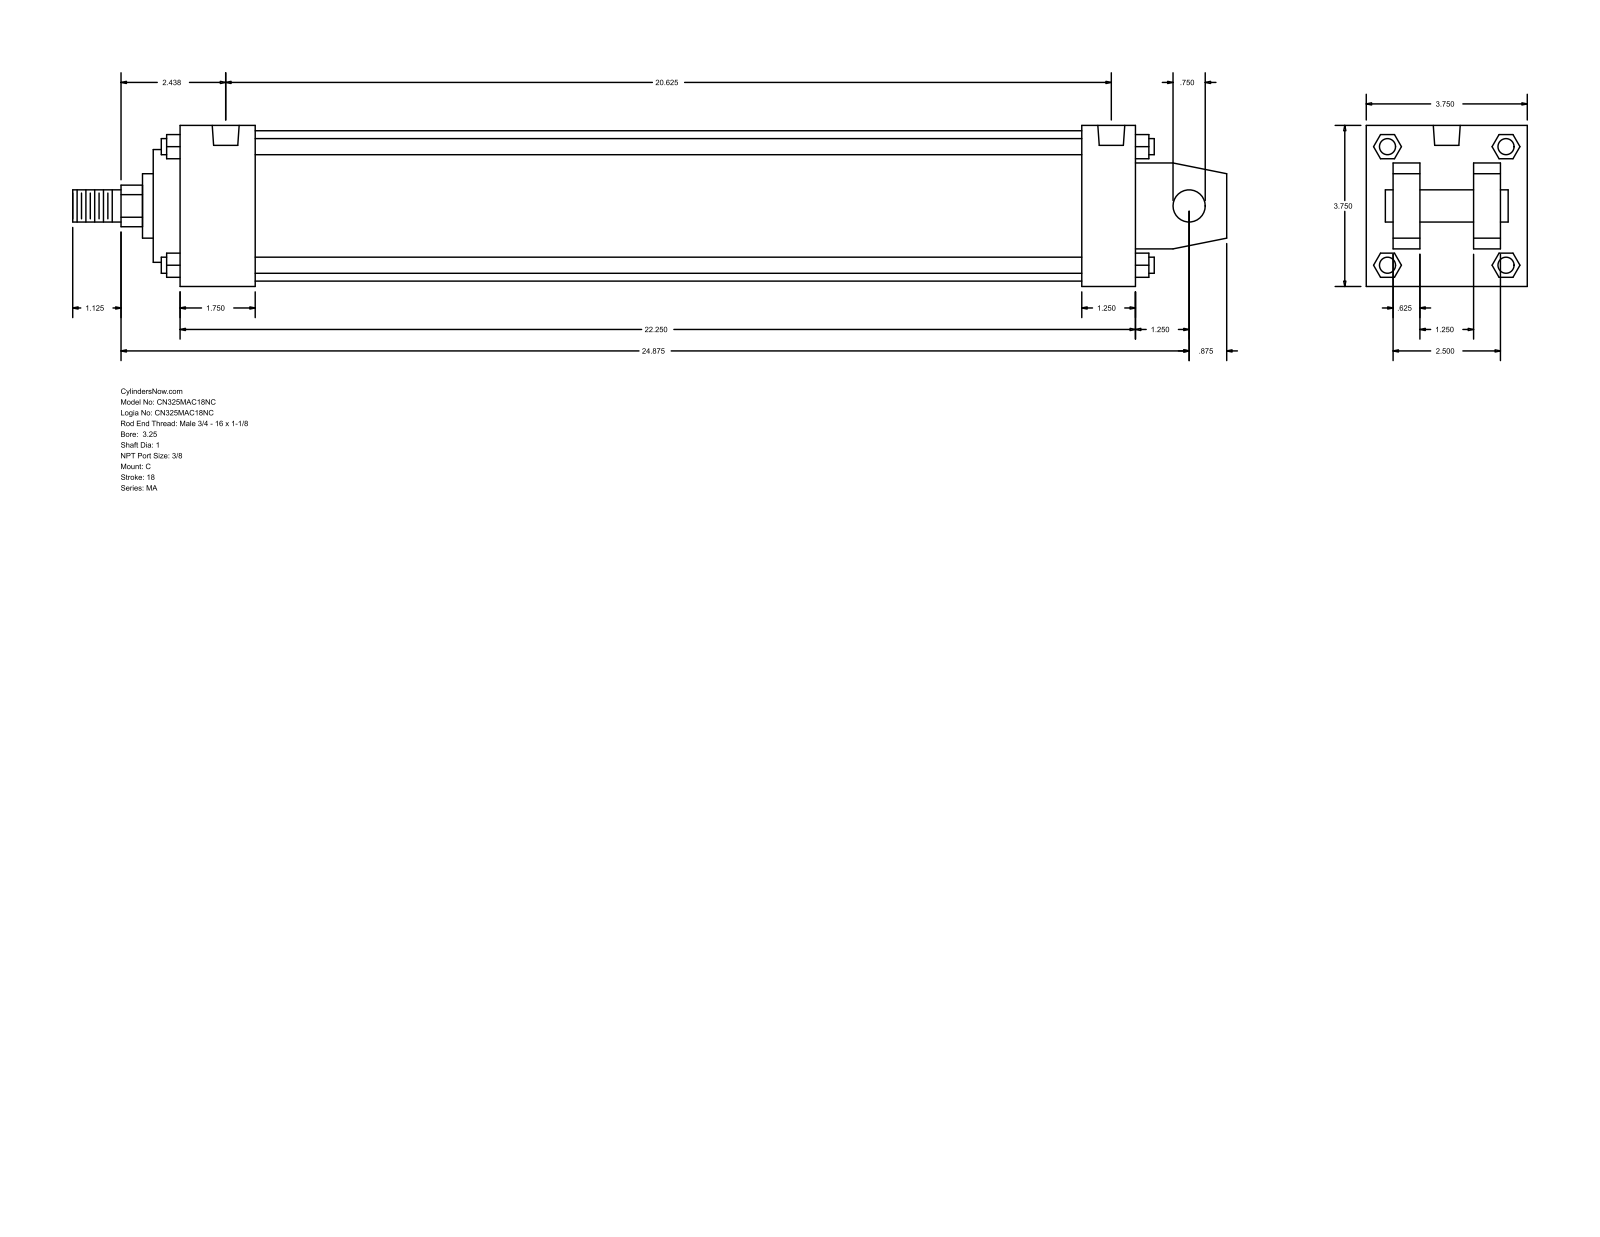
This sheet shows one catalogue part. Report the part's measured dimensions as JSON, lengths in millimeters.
{"part_name": "MA_C__0325_1", "step_written_by": "GSSL Pune (CONFIG_CONTROL_DESIGN)", "units": "millimeters", "bodies": {"solids": 0, "faces": 141, "planar": 109, "cylindrical": 32, "other": 0}, "overall_size": [682.62, 95.25, 95.25], "round_holes": [[11.11, 4], [15.93, 2]], "round_bosses_or_shafts": [[9.53, 4], [19.05, 2], [88.9, 1], [66.67, 1], [38.1, 1], [25.4, 1]], "partial_cylinders_radius": [[12.29, 1]], "face_to_face_distances": [95.24, 15.87, 63.5, 565.16, 31.74, 79.37, 47.63, 533.41, 31.75, 44.46], "hole_center_spacings": [514.35, 4.76, 4.77, 519.11, 519.12, 523.88]}
